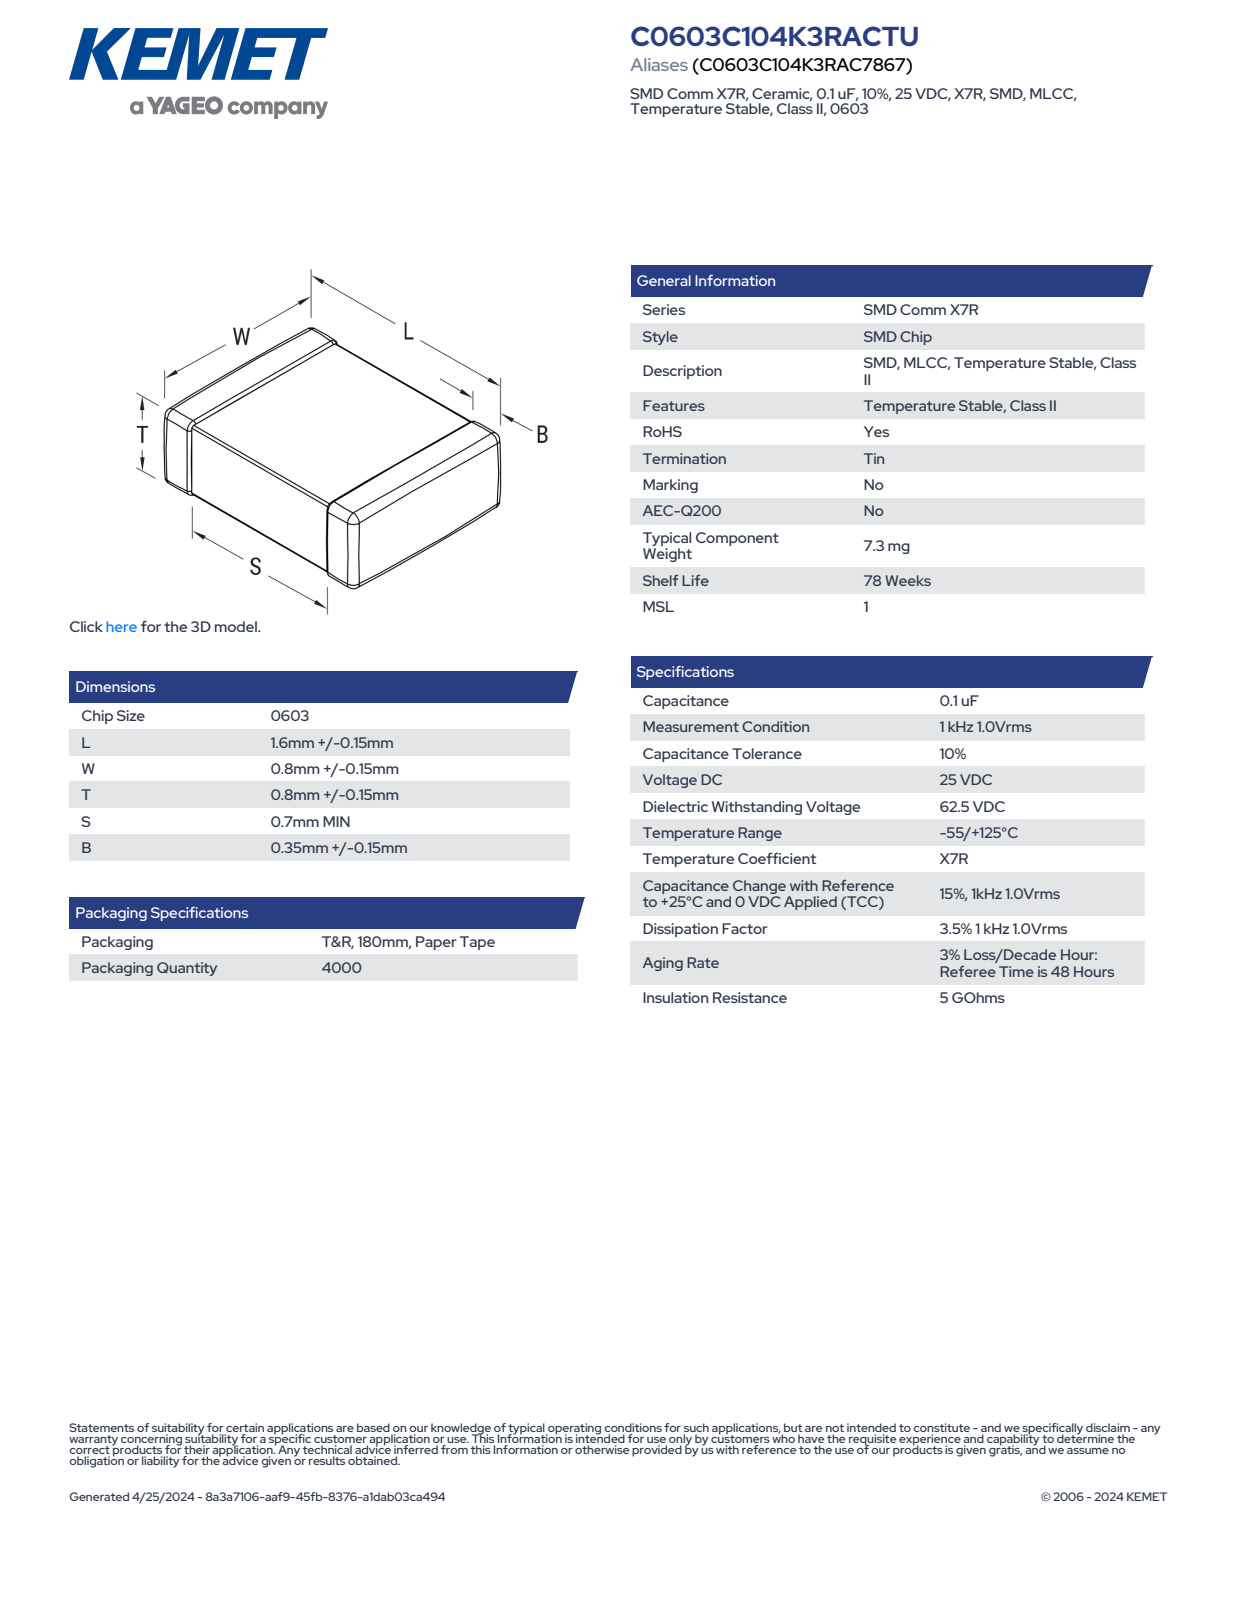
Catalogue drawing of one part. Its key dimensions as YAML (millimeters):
part_name: "CCS_CCSTD_0603_L1.75W0.95T0.95B0.35"
step_written_by: "SolidWorks 2021 (AUTOMOTIVE_DESIGN)"
units: millimeters
bodies: {solids: 4, faces: 125, planar: 71, cylindrical: 38, other: 16}
overall_size: [1.75, 0.95, 0.95]
volume: 2
surface_area: 8
face_to_face_distances: [0.93, 0.95, 0.91, 1.75, 0.94, 0.92, 0.81, 0.8, 0.35, 0.83]
